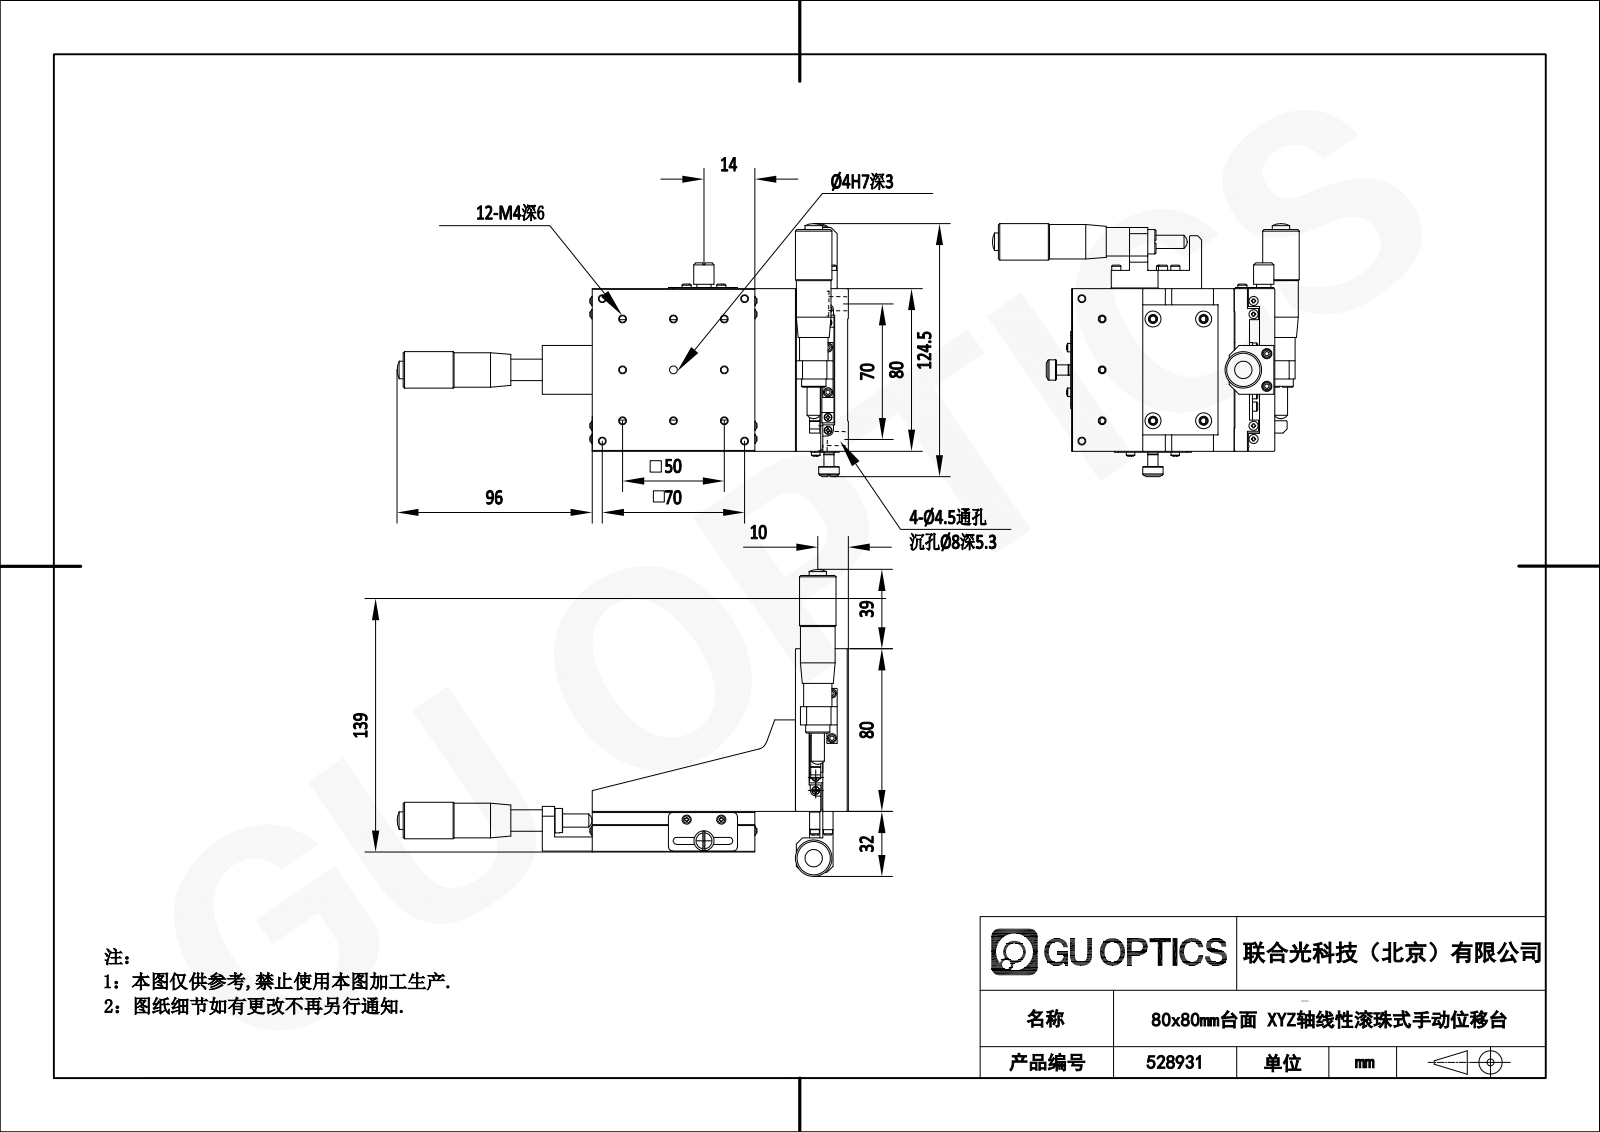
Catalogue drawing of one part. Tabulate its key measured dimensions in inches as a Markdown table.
| quantity | value |
| --- | --- |
| part name | 528931 |
| STEP written by | SolidWorks 2020 (CONFIG_CONTROL_DESIGN) |
| units | inches |
| bodies | 11 solids, 7854 faces (1308 planar, 1665 cylindrical, 4881 other) |
| overall size | 8.563 × 5.99 × 5.084 |
| volume | 25 in³ |
| surface area | 246 in² |
| round holes (diameter × count) | 0.128 × 29, 0.177 × 12, 0.315 × 12, 0.197 × 3, 0.354 × 3, 0.461 × 3, 0.616 × 3, 0.667 × 3, 0.094 × 2, 0.156 × 2, 0.157 × 2, 0.256 × 2 |
| round bosses / shafts (diameter × count) | 0.177 × 16, 0.157 × 8, 0.165 × 4, 0.472 × 3, 0.118 × 3, 0.551 × 2, 0.197 × 2, 0.413 × 1 |
| partial cylindrical surfaces (radius × count) | 0.01 × 50, 0.004 × 24, 0.079 × 12, 0.02 × 4, 0.039 × 4, 0.065 × 4, 0.108 × 4, 0.197 × 3 |
| main face-to-face distances | 0.492, 0.02, 0.315, 0.236, 0.264, 0.531, 0.295, 0.217, 0.512, 0.748 |
| hole center spacings | 0.984, 1.392, 1.433, 2.201, 2.395, 2.735, 1.969, 2.756 |
